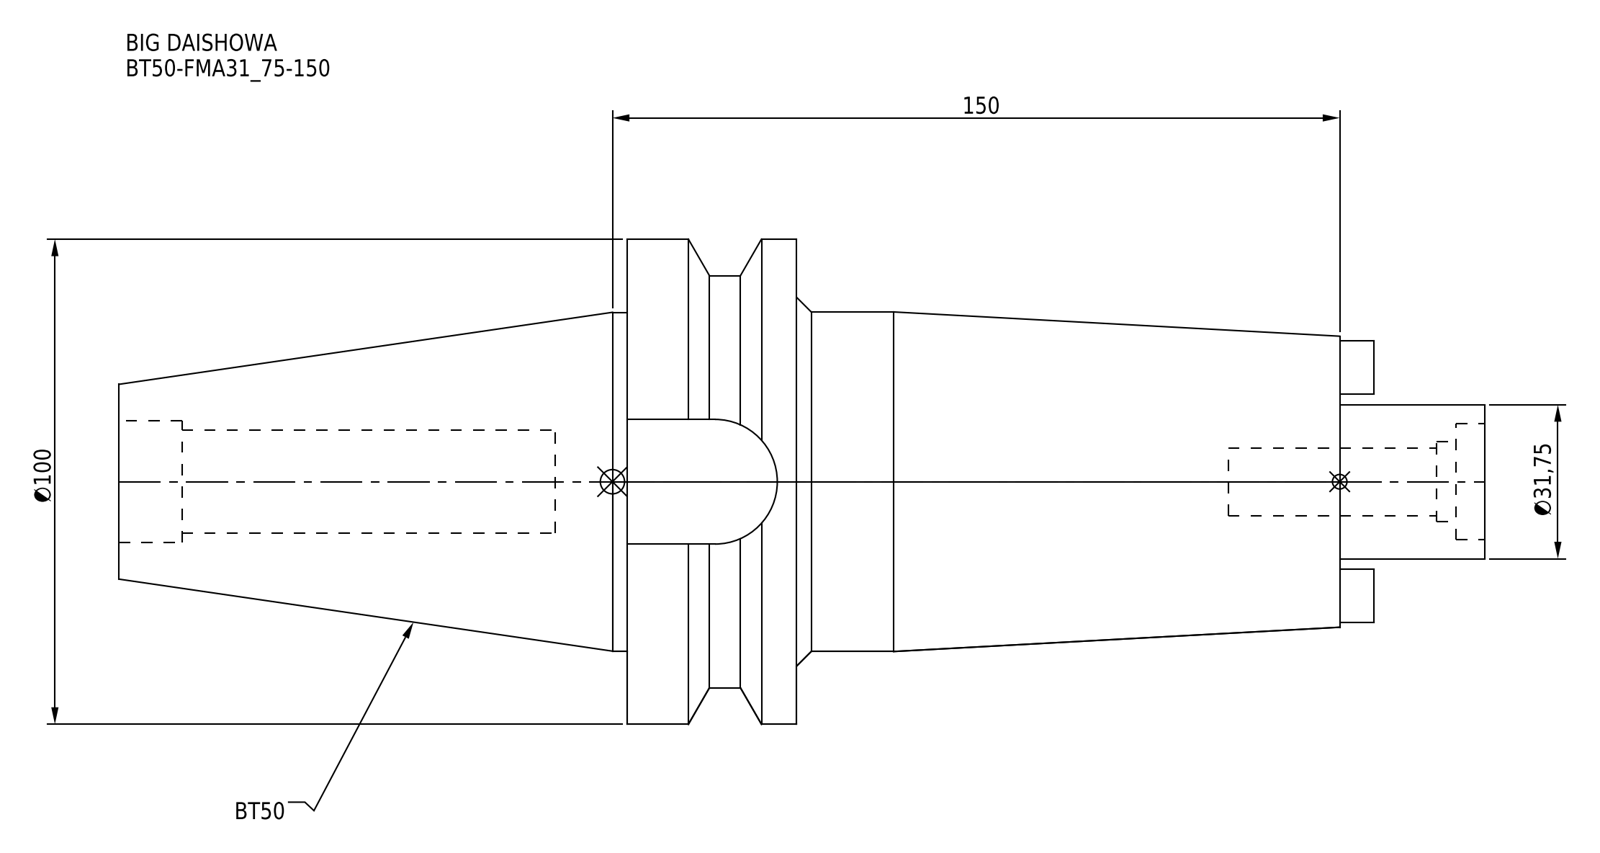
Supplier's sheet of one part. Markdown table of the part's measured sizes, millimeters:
| quantity | value |
| --- | --- |
| part name | BT50-FMA31_75-150 |
| STEP written by | CREO PARAMETRIC BY PTC INC, 2016380 (AUTOMOTIVE_DESIGN) |
| units | millimeters |
| bodies | 1 solid, 62 faces (26 planar, 26 cylindrical, 10 other) |
| overall size | 281.8 × 100 × 100 |
| volume | 859 861 mm³ |
| surface area | 79 309 mm² |
| round holes (diameter × count) | 14 × 1, 16.5 × 1, 21.2 × 1, 24 × 1, 25 × 1 |
| round bosses / shafts (diameter × count) | 100 × 1, 85 × 1, 70 × 1, 69.85 × 1, 31.75 × 1 |
| partial cylindrical surfaces (radius × count) | 12.85 × 1 |
| main face-to-face distances | 35, 112, 147, 251.8, 139.8, 104.8, 70.8, 30, 23, 25.7 |
